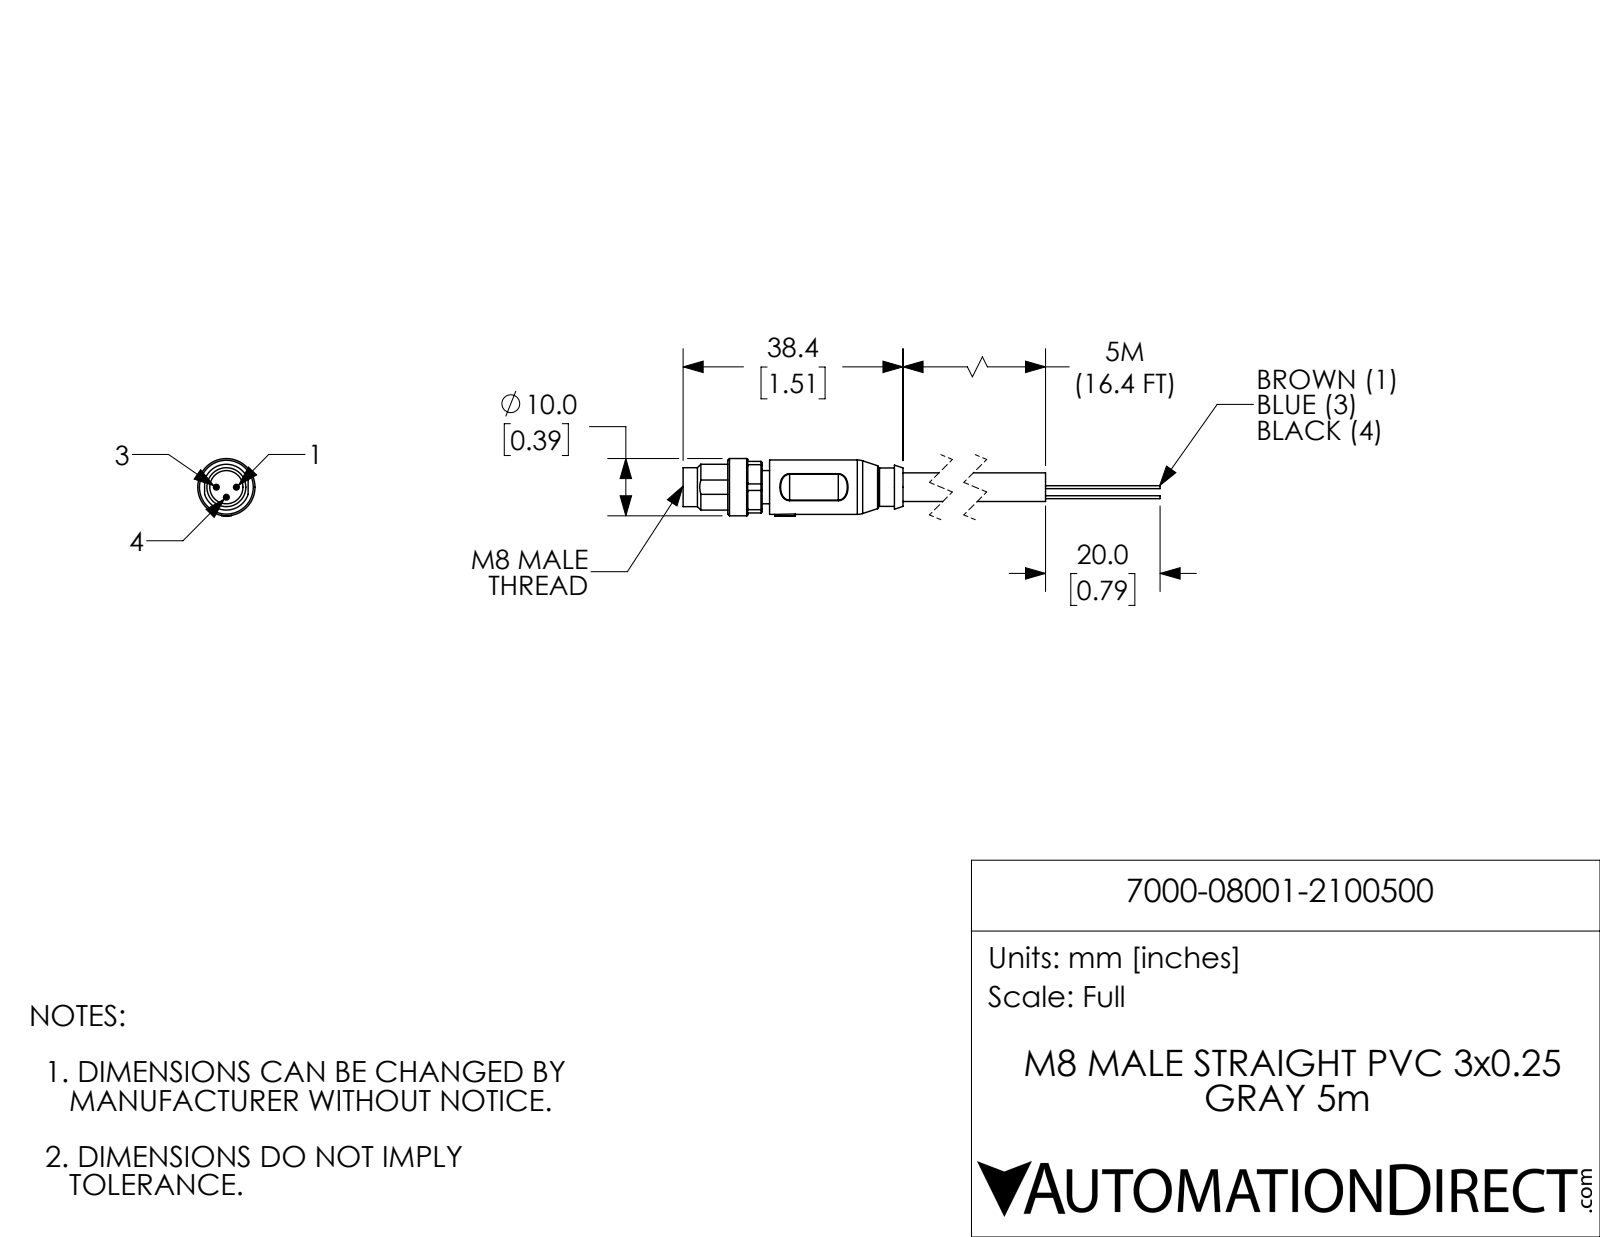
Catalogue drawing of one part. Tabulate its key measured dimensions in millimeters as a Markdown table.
| quantity | value |
| --- | --- |
| part name | 7000-08001-2100500 |
| STEP written by | SolidWorks 2017 (AUTOMOTIVE_DESIGN) |
| units | millimeters |
| bodies | 4 solids, 119 faces (41 planar, 44 cylindrical, 34 other) |
| overall size | 78.4 × 10.05 × 10 |
| volume | 2 535 mm³ |
| surface area | 1 801 mm² |
| round holes (diameter × count) | 5.8 × 1 |
| round bosses / shafts (diameter × count) | 1 × 3, 0.51 × 3, 10 × 1, 9.5 × 1, 8 × 1, 6.8 × 1, 6.7 × 1, 5 × 1 |
| partial cylindrical surfaces (radius × count) | 0.2 × 4, 2.5 × 4, 4.9 × 1, 5.05 × 1 |
| main face-to-face distances | 8.3, 1.3, 9, 0.35, 7.95, 8.8, 10.1, 53.4, 44.6, 43.3 |
